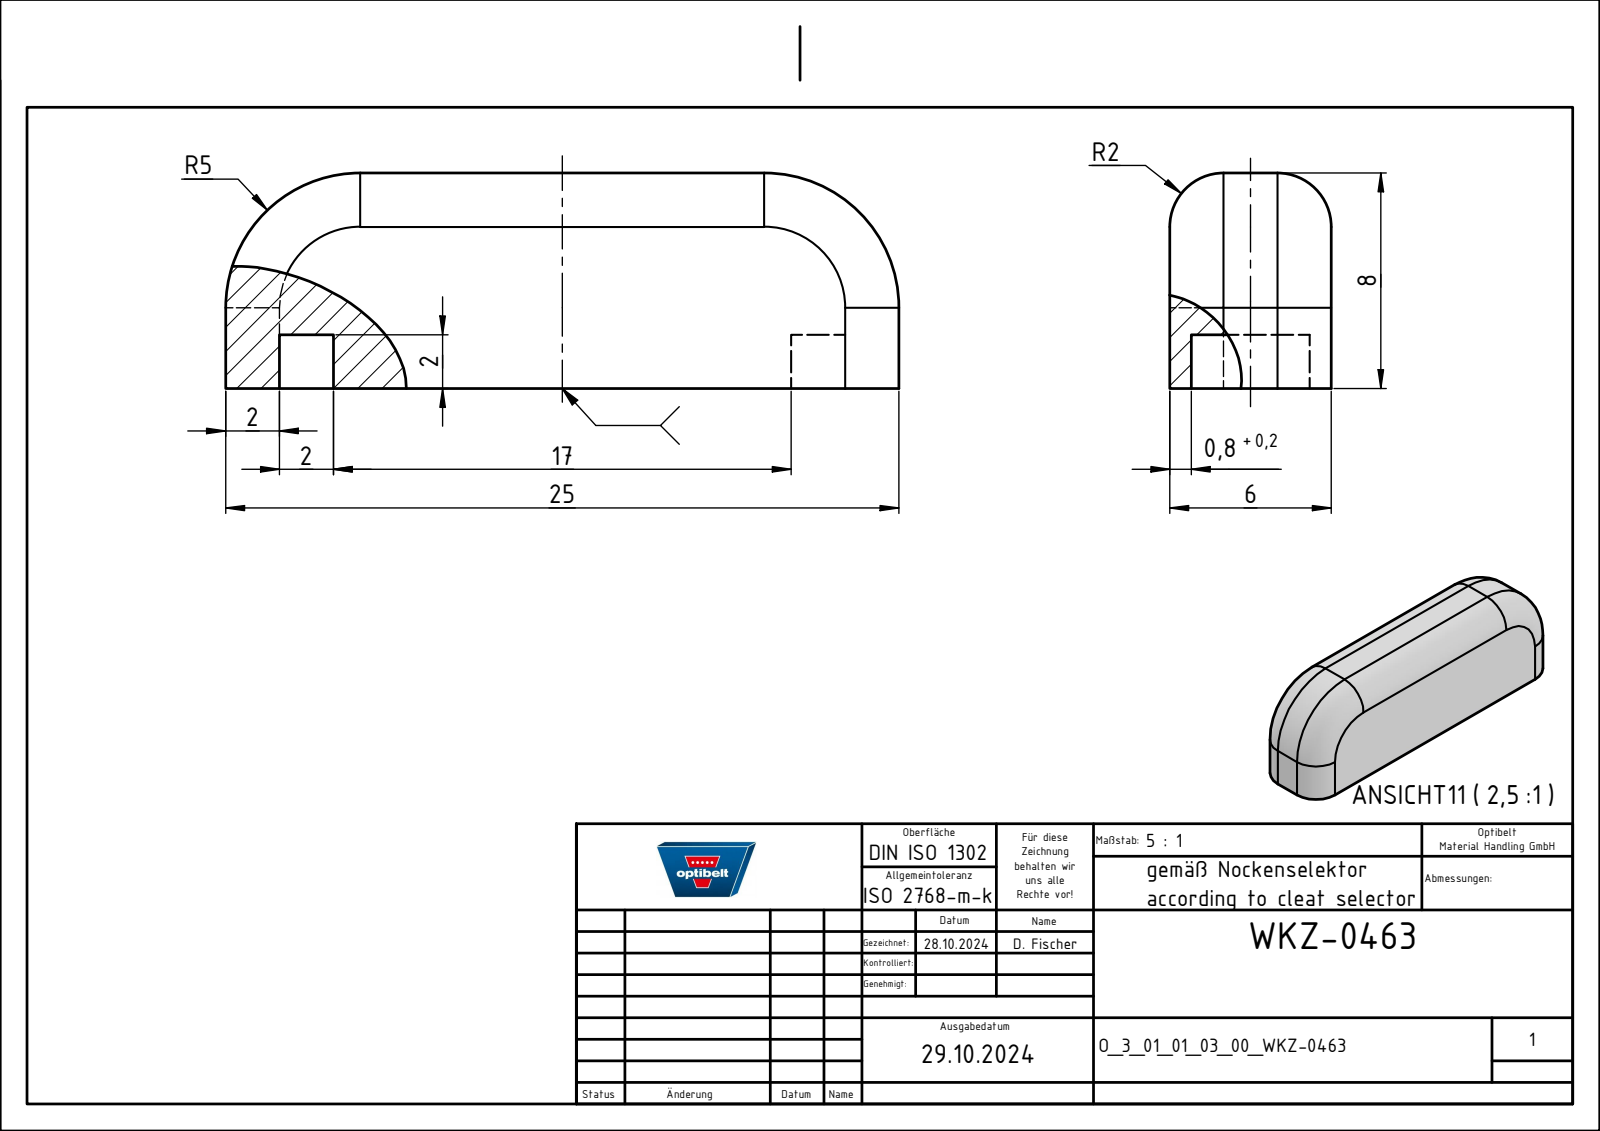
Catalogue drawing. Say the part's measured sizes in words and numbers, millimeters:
The part is named "O_3_01_01_03_00_WKZ-0463". Its 3-D file was written by "Autodesk Inventor 2025 (AUTOMOTIVE_DESIGN)". It is 1 solid with 28 faces: 16 planar, 8 cylindrical and 4 other. Overall it measures 25 by 8 by 6 millimeters. Its volume is 1 040 cubic millimeters and its surface area 732 square millimeters. Partial cylindrical surfaces (rounded edges, fillets, slot ends): 6 of radius 2, 2 of radius 5. The main face-to-face distances are 6, 2, 8, 21, 19, 0.8, 5.2, 4, 23, 17.
